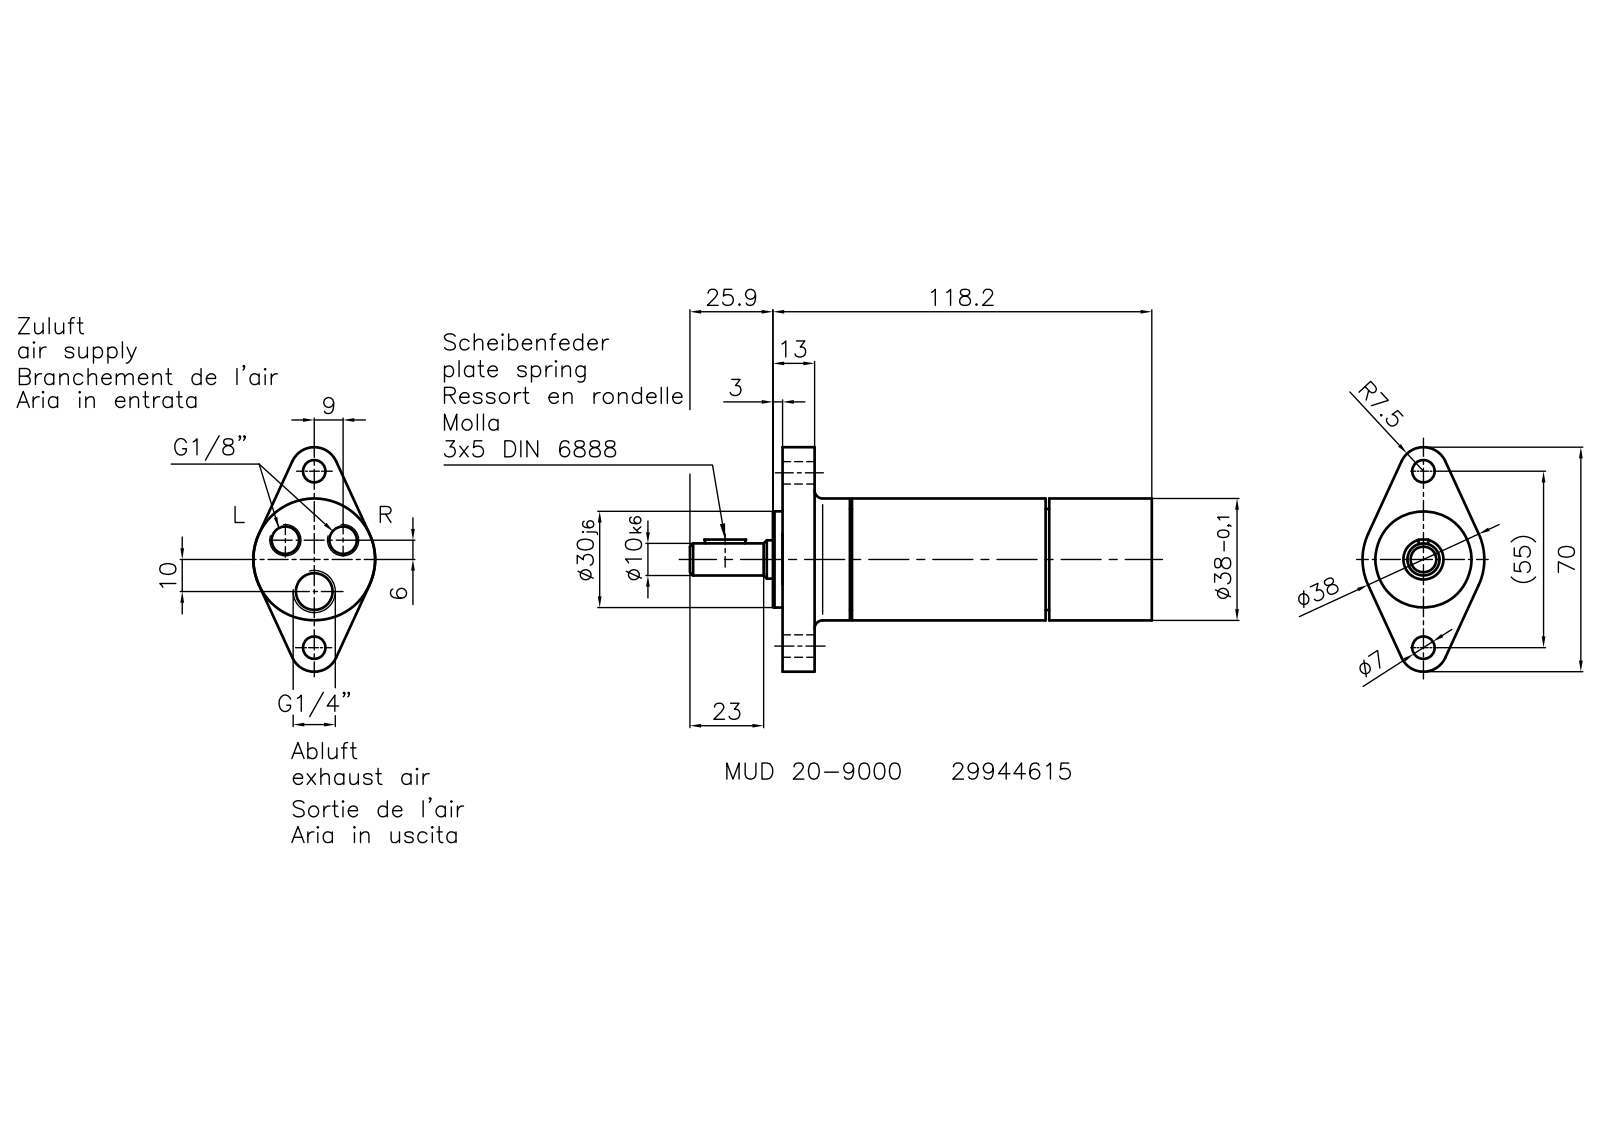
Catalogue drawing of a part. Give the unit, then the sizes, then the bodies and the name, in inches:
Units: inches
Overall size (bounding box): 5.594 × 2.756 × 1.496
Round holes (diameter × count): ⌀0.276 ×2, ⌀0.492 ×1
Round bosses / shafts (diameter × count): ⌀1.496 ×1, ⌀1.449 ×1, ⌀1.181 ×1, ⌀0.467 ×1, ⌀0.394 ×1
Partial cylindrical surfaces — rounded edges, fillets, slot ends (radius × count): R0.295 ×2, R0.256 ×1, R0.266 ×1
Main face-to-face distances: 4.535, 0.118, 4.654, 1.495, 0.512, 0.394, 4.142, 4.193, 4.075, 3.681
Hole centre spacings: 1.083, 2.165
Volume: 8.395 in³ · Surface area: 31.84 in²
Bodies: 1 solid, 55 faces (24 planar, 15 cylindrical, 16 other)
Part name (STEP PRODUCT): MUD 20-9000_29944615
STEP written by: Autodesk Inventor 2008 (CONFIG_CONTROL_DESIGN)
